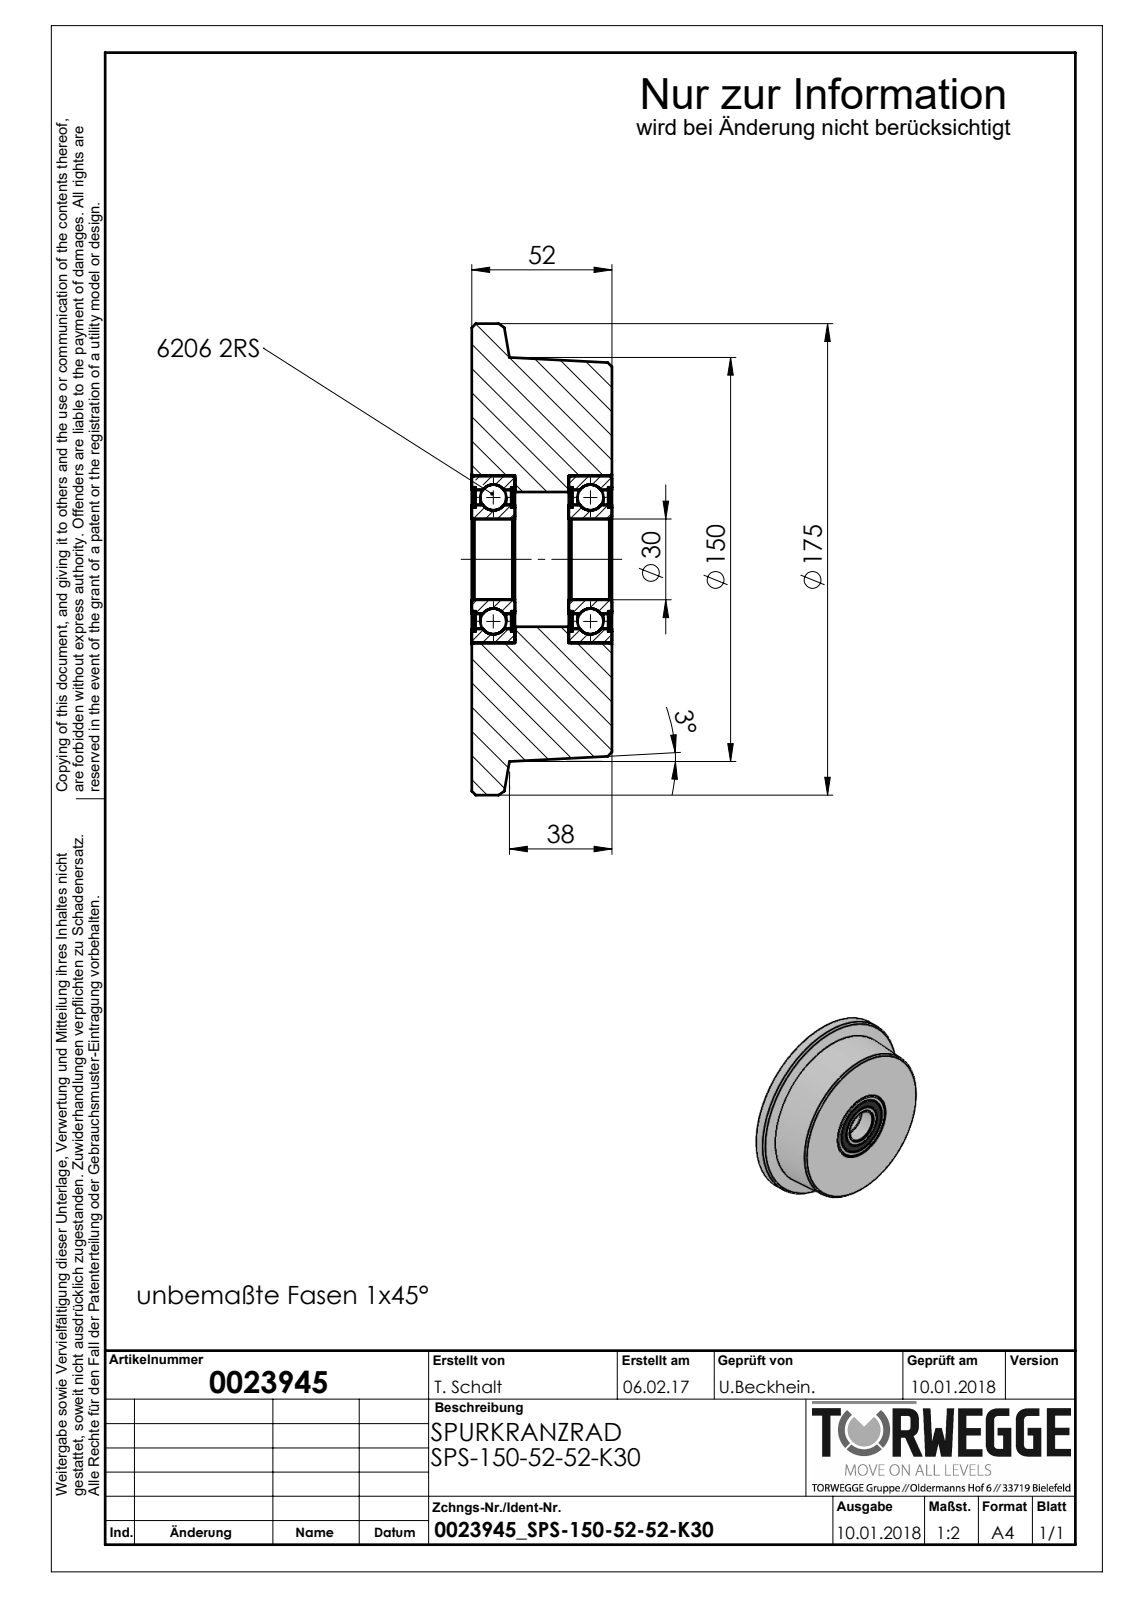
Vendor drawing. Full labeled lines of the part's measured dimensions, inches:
Part name (STEP PRODUCT): 0023945_SPS-150-52-52-K30
STEP written by: SolidWorks 2016 (AUTOMOTIVE_DESIGN)
Units: inches
Bodies: 0 solids, 31 faces (12 planar, 8 cylindrical, 11 other)
Overall size (bounding box): 6.89 × 6.89 × 2.047
Round holes (diameter × count): ⌀1.181 ×1, ⌀1.969 ×1
Round bosses / shafts (diameter × count): ⌀6.89 ×1, ⌀2.441 ×1
Main face-to-face distances: 2.047
